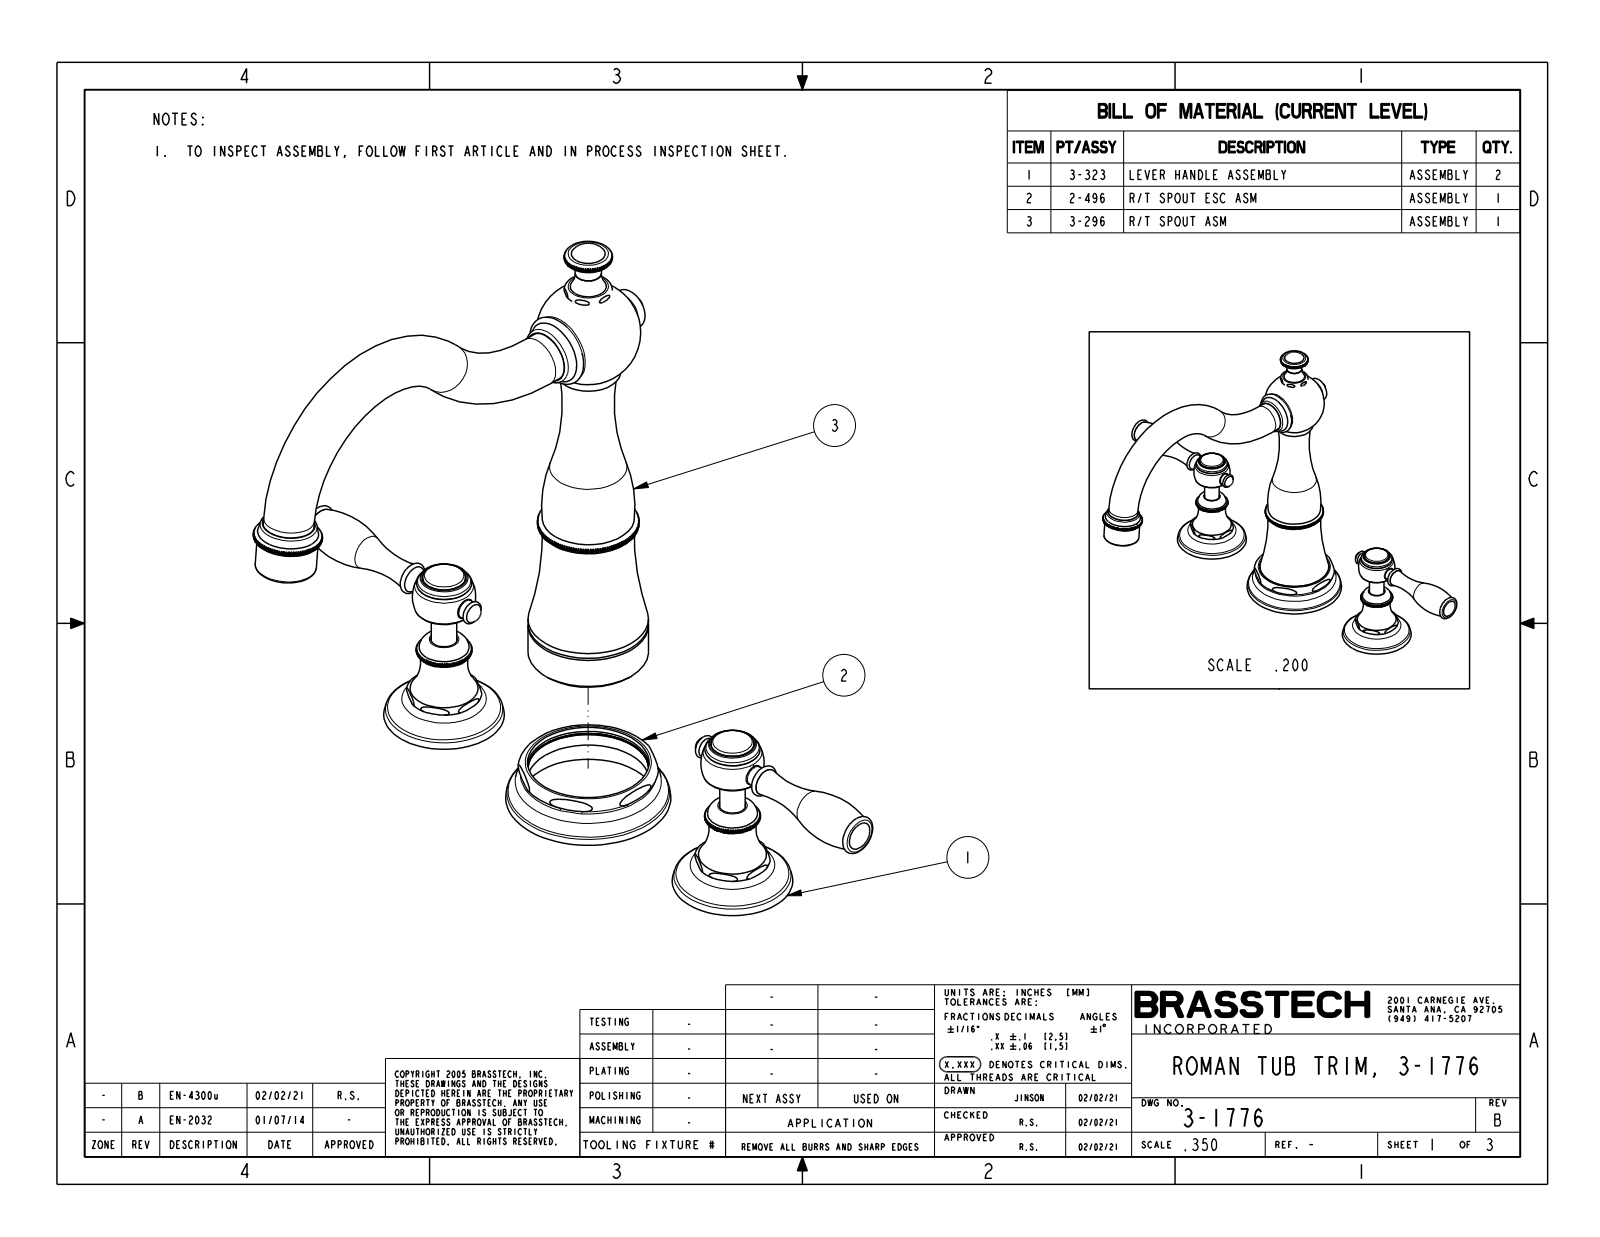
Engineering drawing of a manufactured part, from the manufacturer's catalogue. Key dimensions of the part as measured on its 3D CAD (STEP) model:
Part name (STEP PRODUCT): 3-1776
STEP written by: CREO PARAMETRIC BY PTC INC, 2018400 (CONFIG_CONTROL_DESIGN)
Units: inches
Bodies: 3 solids, 1099 faces (883 planar, 34 cylindrical, 182 other)
Overall size (bounding box): 15.292 × 10.631 × 10.171
Volume: 41.56 in³ · Surface area: 154.9 in²
Round holes (diameter × count): ⌀0.855 ×2, ⌀0.41 ×1
Round bosses / shafts (diameter × count): ⌀1 ×2, ⌀0.84 ×2, ⌀0.5 ×2, ⌀1.2 ×1, ⌀0.392 ×1
Main face-to-face distances: 2.54, 1.375, 0.85, 1.69, 2.617, 4, 8, 6.216, 8.833, 2.617
Hole centre spacings: 8
